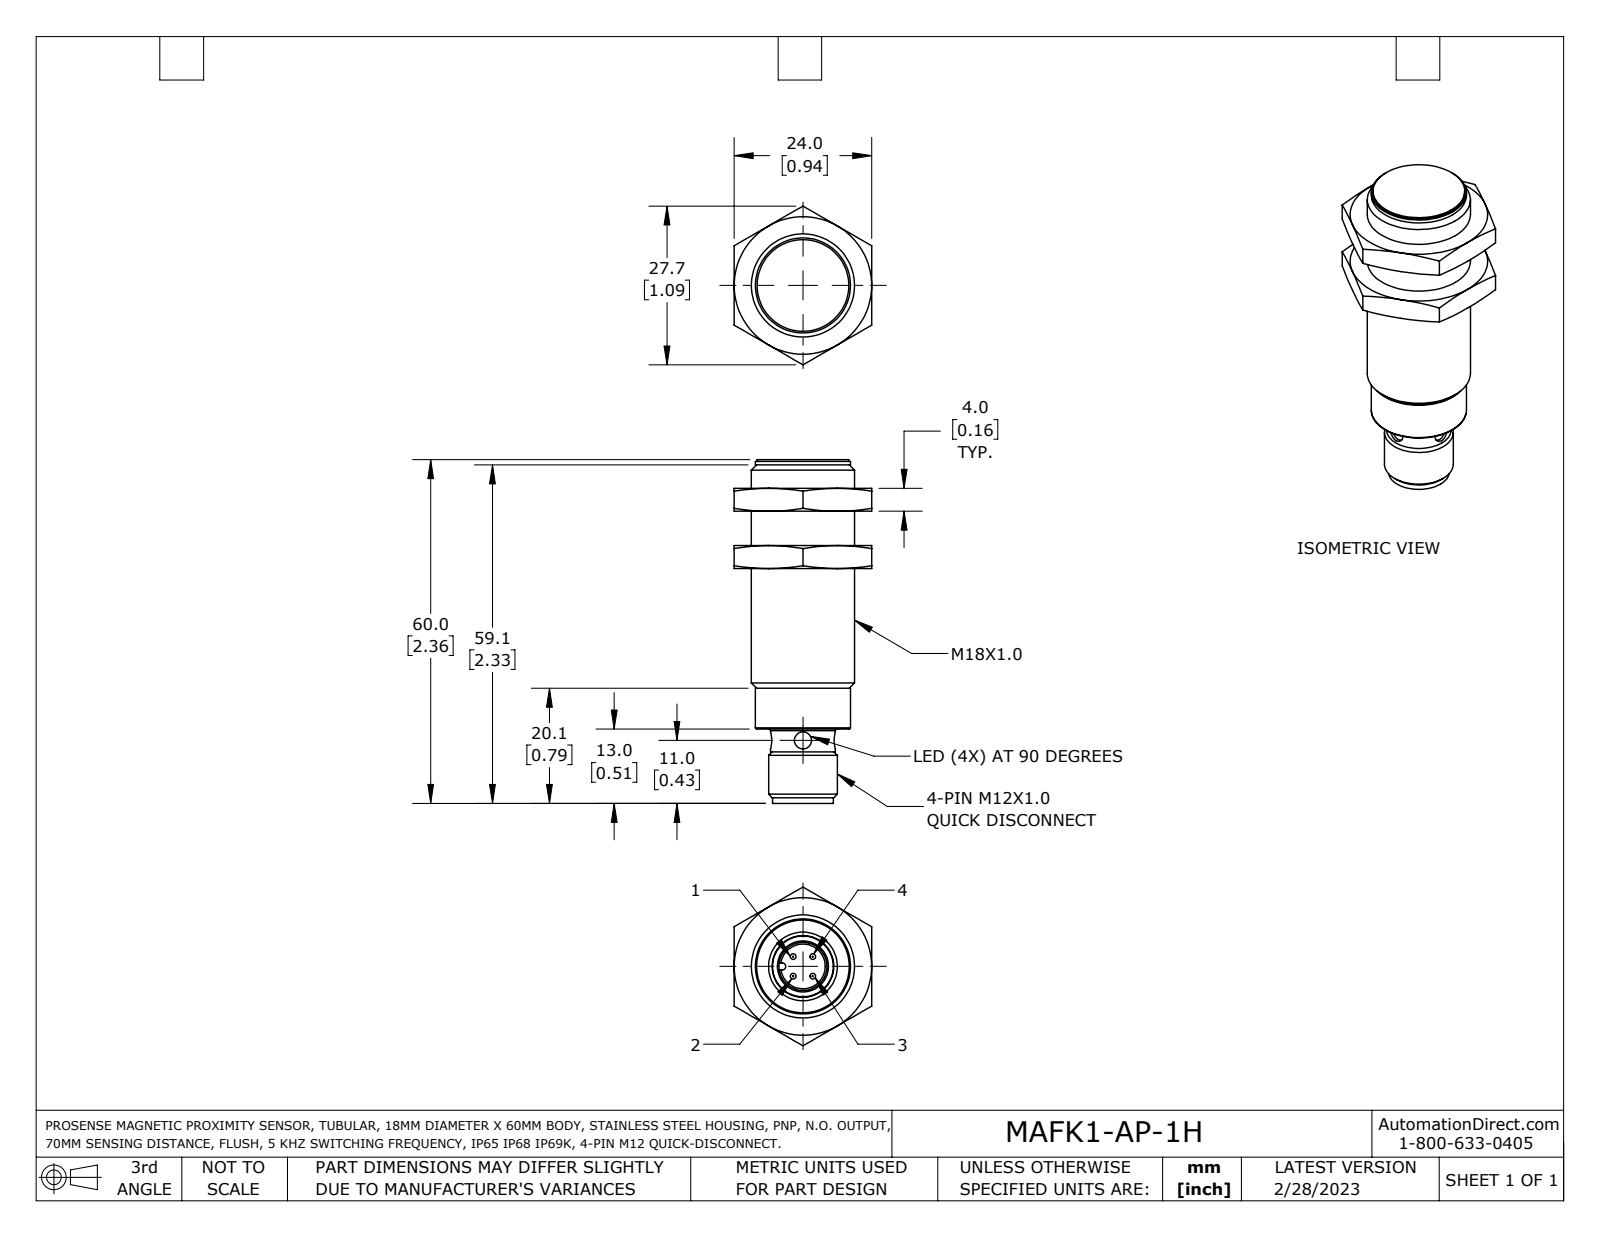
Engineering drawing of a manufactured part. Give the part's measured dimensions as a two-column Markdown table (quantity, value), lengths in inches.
| quantity | value |
| --- | --- |
| part name | MAFK1-AP-1H |
| STEP written by | SolidWorks 2021 (AUTOMOTIVE_DESIGN) |
| units | inches |
| bodies | 1 solid, 42 faces (26 planar, 16 cylindrical, 0 other) |
| overall size | 3.425 × 3.15 × 1.949 |
| volume | 2.354 in³ |
| surface area | 54.21 in² |
| round holes (diameter × count) | 0.256 × 4 |
| partial cylindrical surfaces (radius × count) | 0.059 × 2, 0.098 × 2, 0.157 × 2 |
| main face-to-face distances | 0.098, 3.327, 3.425, 3.228, 1.033, 0.049, 1.083, 0.984, 2.067, 2.116 |
| hole center spacings | 2.559, 3.619 |
